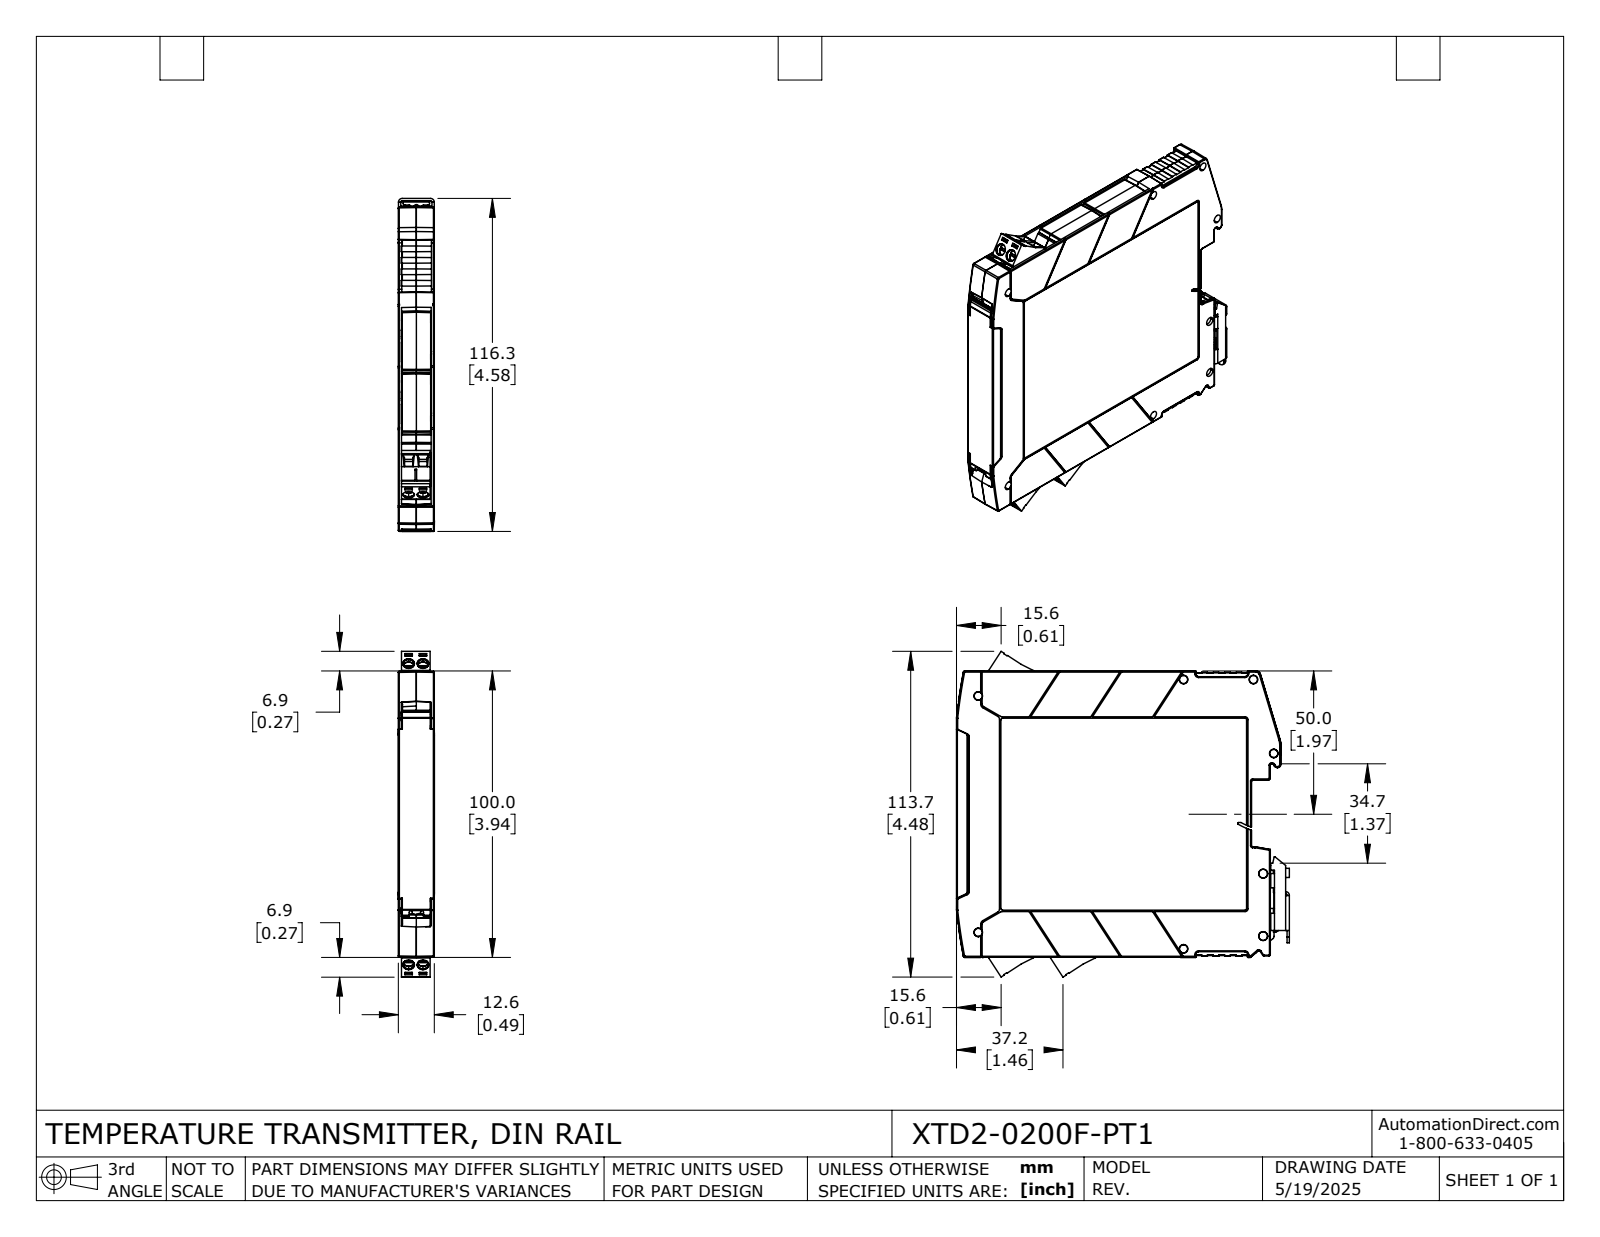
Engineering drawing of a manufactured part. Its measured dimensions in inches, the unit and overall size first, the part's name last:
Units: inches
Overall size (bounding box): 4.577 × 4.478 × 0.496
Round holes (diameter × count): ⌀0.063 ×6, ⌀0.11 ×6, ⌀0.152 ×6, ⌀0.159 ×6
Round bosses / shafts (diameter × count): ⌀0.156 ×6, ⌀0.098 ×6, ⌀0.059 ×2, ⌀0.053 ×2
Partial cylindrical surfaces — rounded edges, fillets, slot ends (radius × count): R0.008 ×89, R0.012 ×78, R0.02 ×71, R0.039 ×22, R0.004 ×20, R0.016 ×13, R0.006 ×12, R0.028 ×8
Main face-to-face distances: 0.049, 0.445, 0.494, 0.396, 0.043, 0.451, 0.402, 0.031, 0.198, 0.247
Hole centre spacings: 0.197, 0.464, 0.504, 0.713, 0.739
Volume: 2.41 in³ · Surface area: 101.5 in²
Bodies: 14 solids, 3337 faces (1910 planar, 596 cylindrical, 831 other)
Part name (STEP PRODUCT): XTD2-0200F-PT1
STEP written by: SolidWorks 2024 (AUTOMOTIVE_DESIGN)
